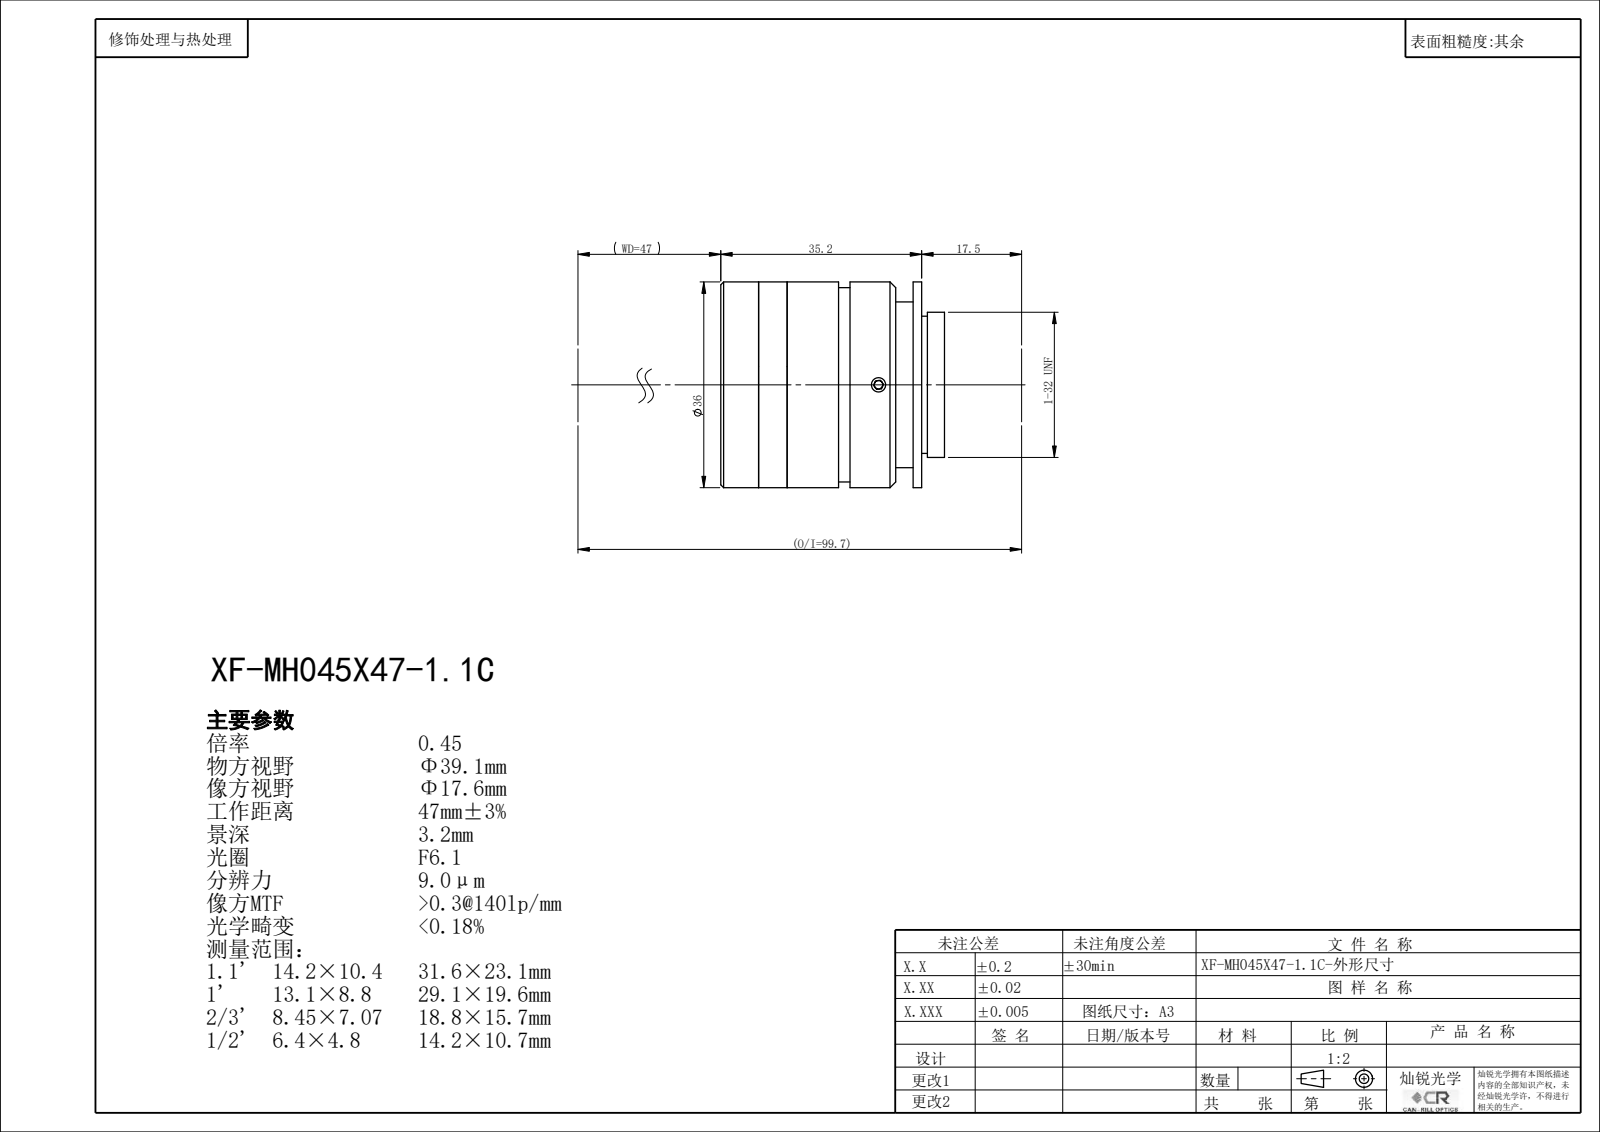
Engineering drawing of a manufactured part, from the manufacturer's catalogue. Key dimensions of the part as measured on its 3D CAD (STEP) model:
Part name (STEP PRODUCT): XF-MH045X47-1.1C
STEP written by: SolidWorks 2022 (CONFIG_CONTROL_DESIGN)
Units: millimetres
Bodies: 0 solids, 105 faces (48 planar, 36 cylindrical, 21 other)
Overall size (bounding box): 39.17 × 36 × 36
Round holes (diameter × count): ⌀2.5 ×3, ⌀10 ×1, ⌀15 ×1, ⌀17.4 ×1, ⌀21.5 ×1, ⌀24.9 ×1, ⌀26 ×1
Round bosses / shafts (diameter × count): ⌀36 ×1, ⌀34 ×1, ⌀29 ×1, ⌀25.4 ×1, ⌀24 ×1
Main face-to-face distances: 5, 28.55, 23.55, 6.62, 11.62, 35.17, 1.5, 33.67, 27.05, 22.05
